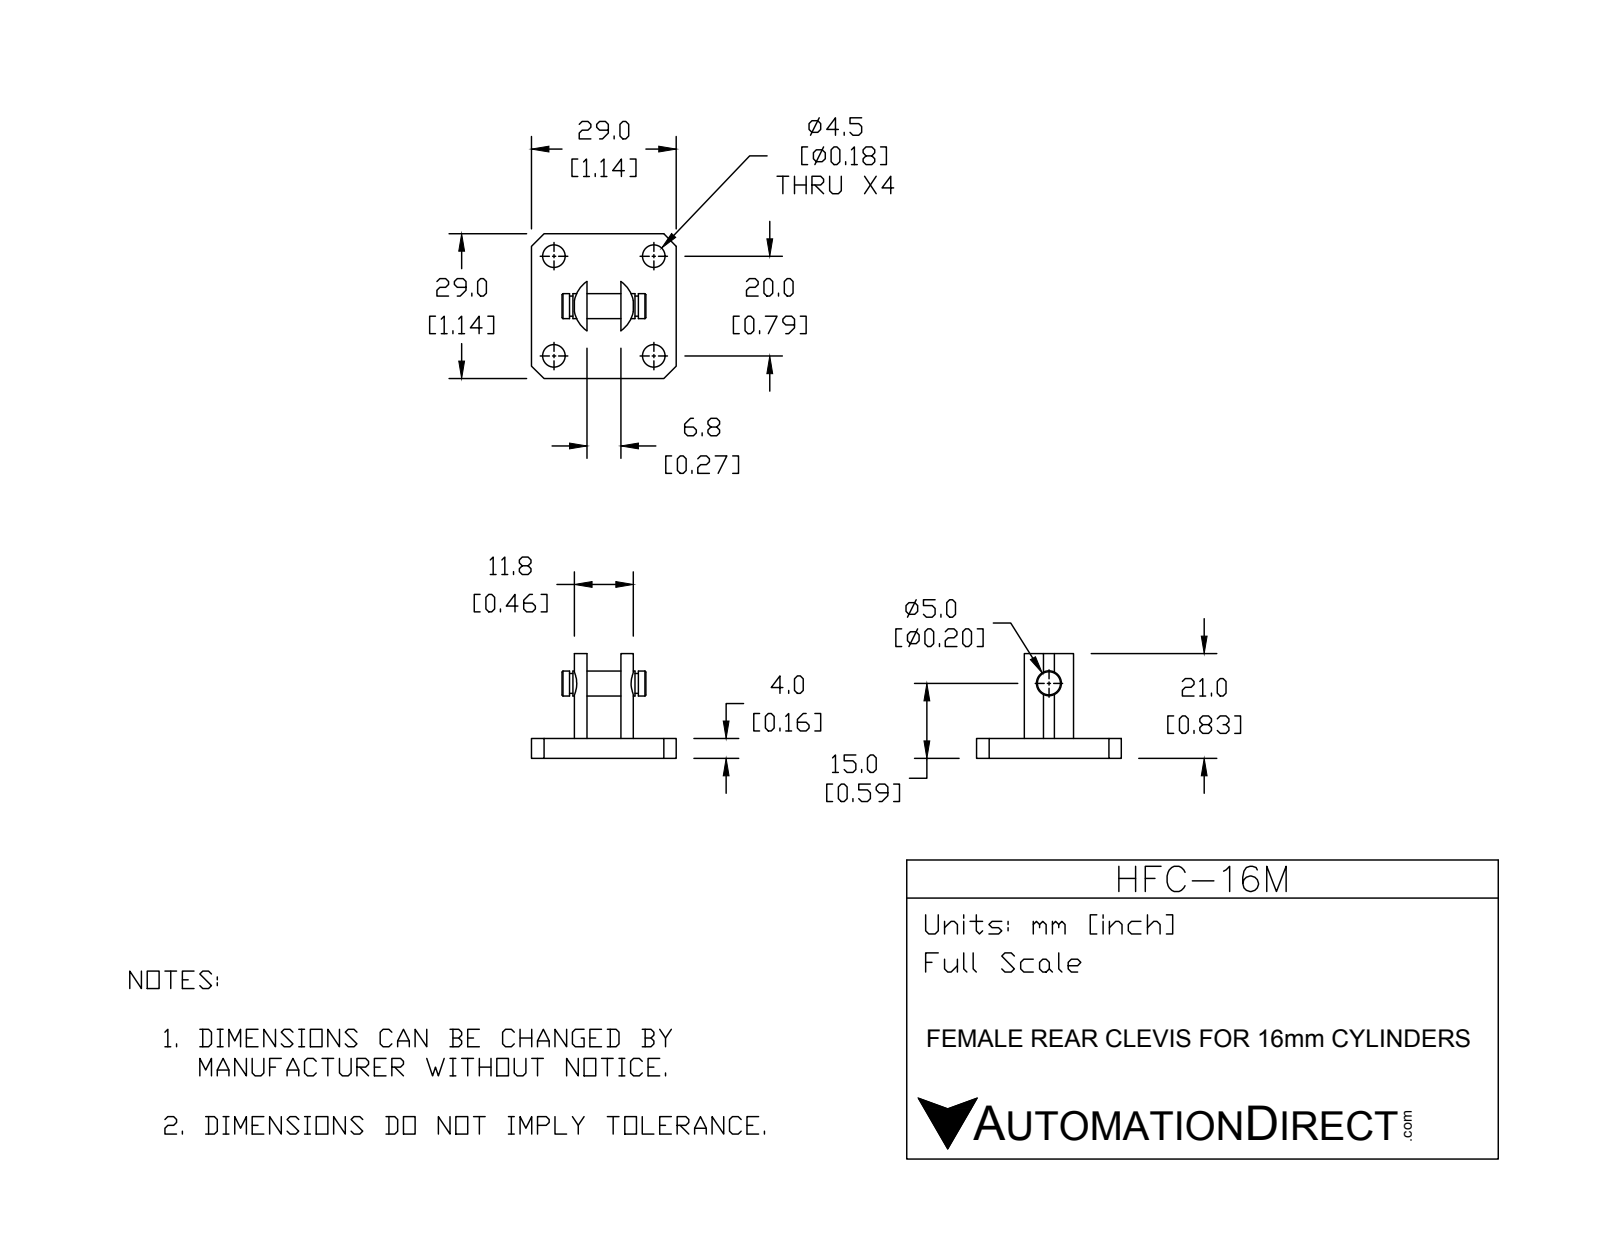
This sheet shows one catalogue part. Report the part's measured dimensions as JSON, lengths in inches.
{"part_name": "HFC-16M", "step_written_by": "SolidWorks 2015 (CONFIG_CONTROL_DESIGN)", "units": "inches", "bodies": {"solids": 2, "faces": 54, "planar": 24, "cylindrical": 26, "other": 4}, "overall_size": [1.142, 1.142, 0.827], "volume_in3": 0.238, "surface_area_in2": 5.028, "round_holes": [[0.177, 4]], "round_bosses_or_shafts": [[0.197, 1], [0.157, 1]], "partial_cylinders_radius": [[0.236, 1]], "face_to_face_distances": [0.157, 0.437, 0.705, 1.142, 0.268, 0.098, 0.465, 0.339, 0.803, 0.366], "hole_center_spacings": [0.787, 1.113]}
